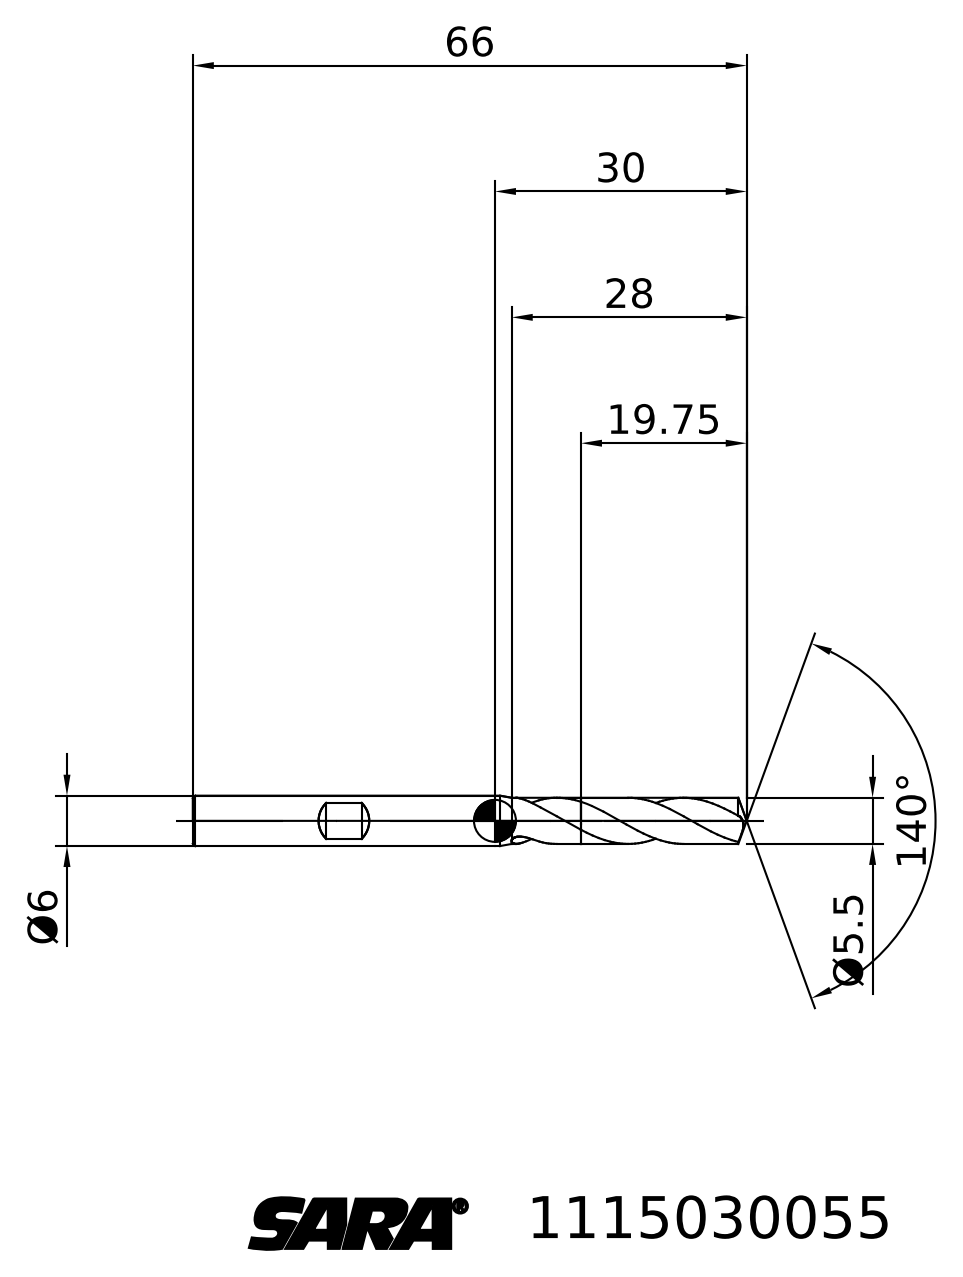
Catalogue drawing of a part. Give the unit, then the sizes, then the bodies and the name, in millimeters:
Units: millimetres
Overall size (bounding box): 66 × 13.11 × 8.62
Main face-to-face distances: 46.25
Volume: 1 511 mm³ · Surface area: 1 299 mm²
Bodies: 2 solids, 27 faces (3 planar, 0 cylindrical, 24 other)
STEP written by: TDM (AUTOMOTIVE_DESIGN)
